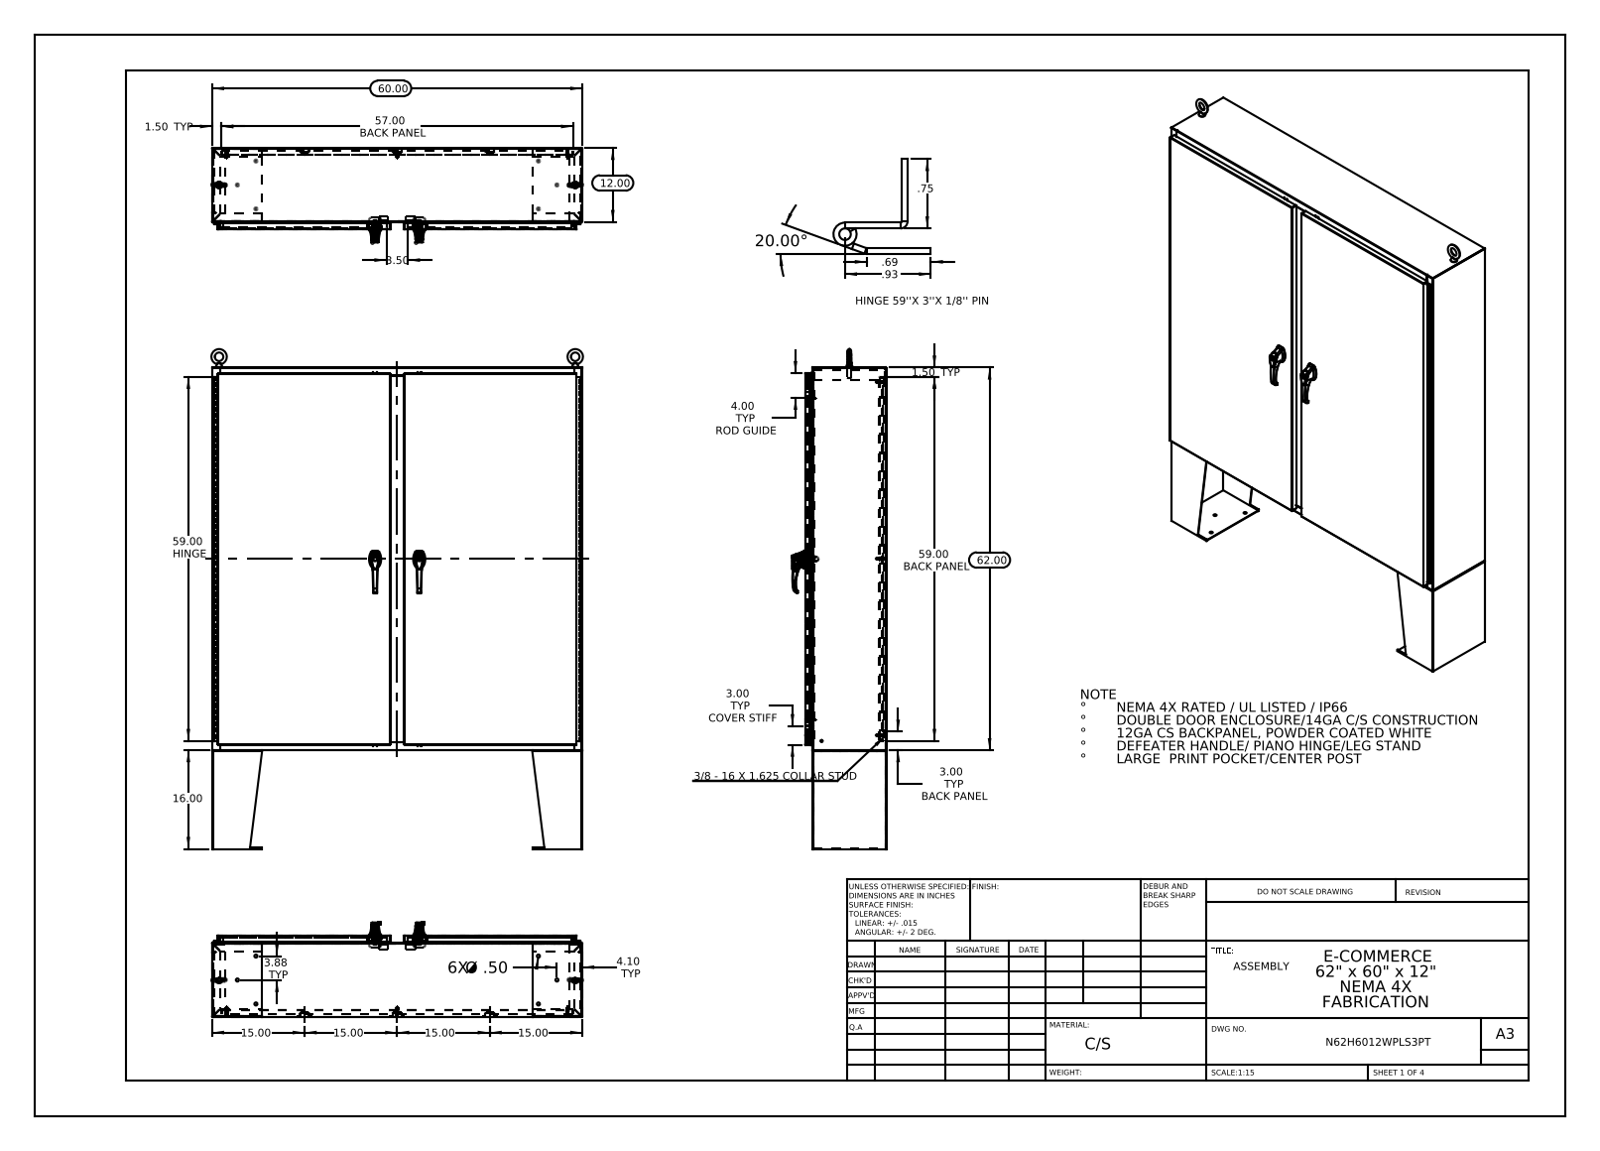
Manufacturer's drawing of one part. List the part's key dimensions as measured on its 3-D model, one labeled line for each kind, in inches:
Part name (STEP PRODUCT): N62H6012SSWPLS3PT Hinge Enclosure Side DoubleDoor; Mounting Studs; 26161102; Defeater Handle - 3 - 2500-51 ZN (+8 more)
STEP written by: SolidWorks 2013 (CONFIG_CONTROL_DESIGN)
Units: inches
Bodies: 82 solids, 7016 faces (2786 planar, 2770 cylindrical, 1460 other)
Overall size (bounding box): 81 × 60.226 × 15.307
Volume: 1 439 in³ · Surface area: 34 813 in²
Round holes (diameter × count): ⌀0.25 ×20, ⌀0.5 ×14, ⌀0.138 ×6, ⌀0.161 ×6, ⌀0.079 ×4, ⌀0.313 ×4, ⌀0.437 ×4, ⌀0.75 ×4, ⌀0.125 ×2, ⌀0.125 ×2, ⌀0.197 ×2, ⌀0.203 ×2
Round bosses / shafts (diameter × count): ⌀0.157 ×12, ⌀0.14 ×12, ⌀0.625 ×10, ⌀0.375 ×8, ⌀0.33 ×8, ⌀0.315 ×5, ⌀0.236 ×5, ⌀1.181 ×2
Partial cylindrical surfaces — rounded edges, fillets, slot ends (radius × count): R0.118 ×72, R0.006 ×66, R0.013 ×46, R0.088 ×38, R0.039 ×28, R0.028 ×24, R0.008 ×12, R0.02 ×12
Main face-to-face distances: 0.075, 13.126, 0.104, 13.051, 1.075, 13.201, 1, 12.051, 12.126, 1.179
Hole centre spacings: 7.152, 24.366, 0.295, 0.625, 0.841, 1.313, 1.561, 7.117
